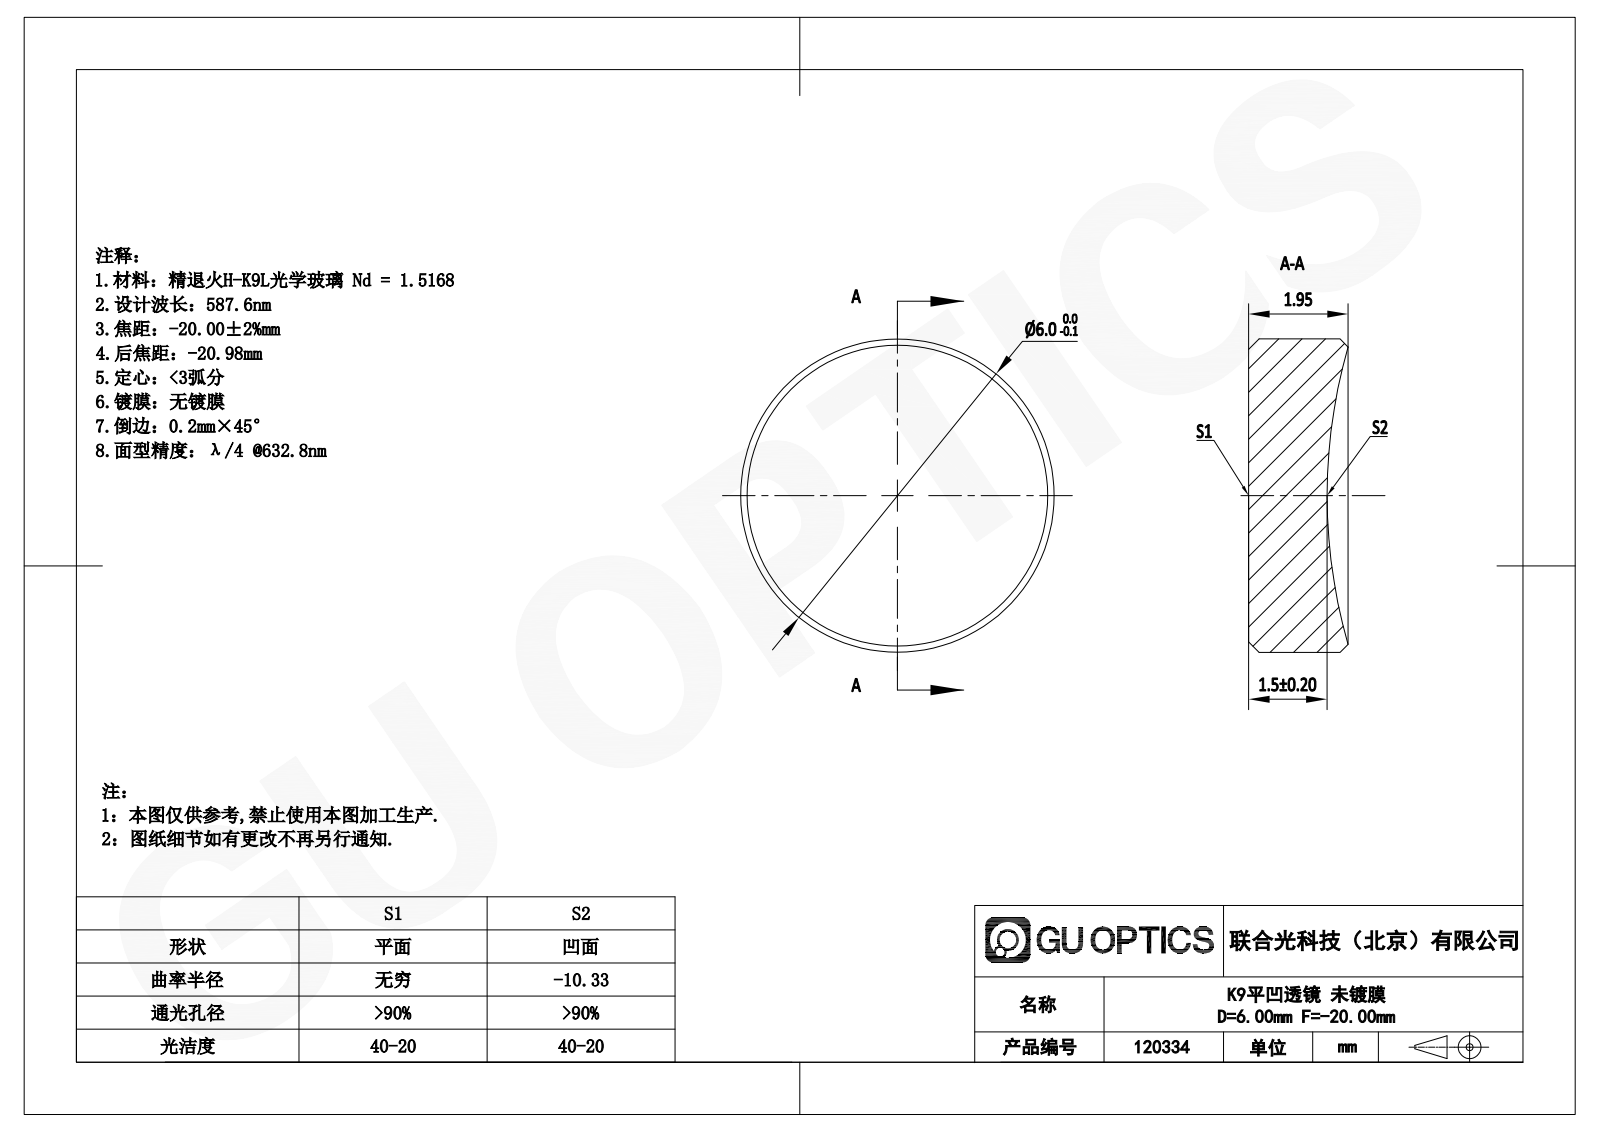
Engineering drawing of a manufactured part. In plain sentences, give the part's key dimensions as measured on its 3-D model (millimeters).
The part is named "GL13-006A-020". Its 3-D file was written by "SolidWorks 2022 (AUTOMOTIVE_DESIGN)". It is 1 solid with 9 faces: 1 planar, 2 cylindrical and 6 other. Overall it measures 6 by 6 by 1.9 millimeters. Its volume is 48 cubic millimeters and its surface area 89 square millimeters. Round bosses or shafts: 1 of diameter 6.
